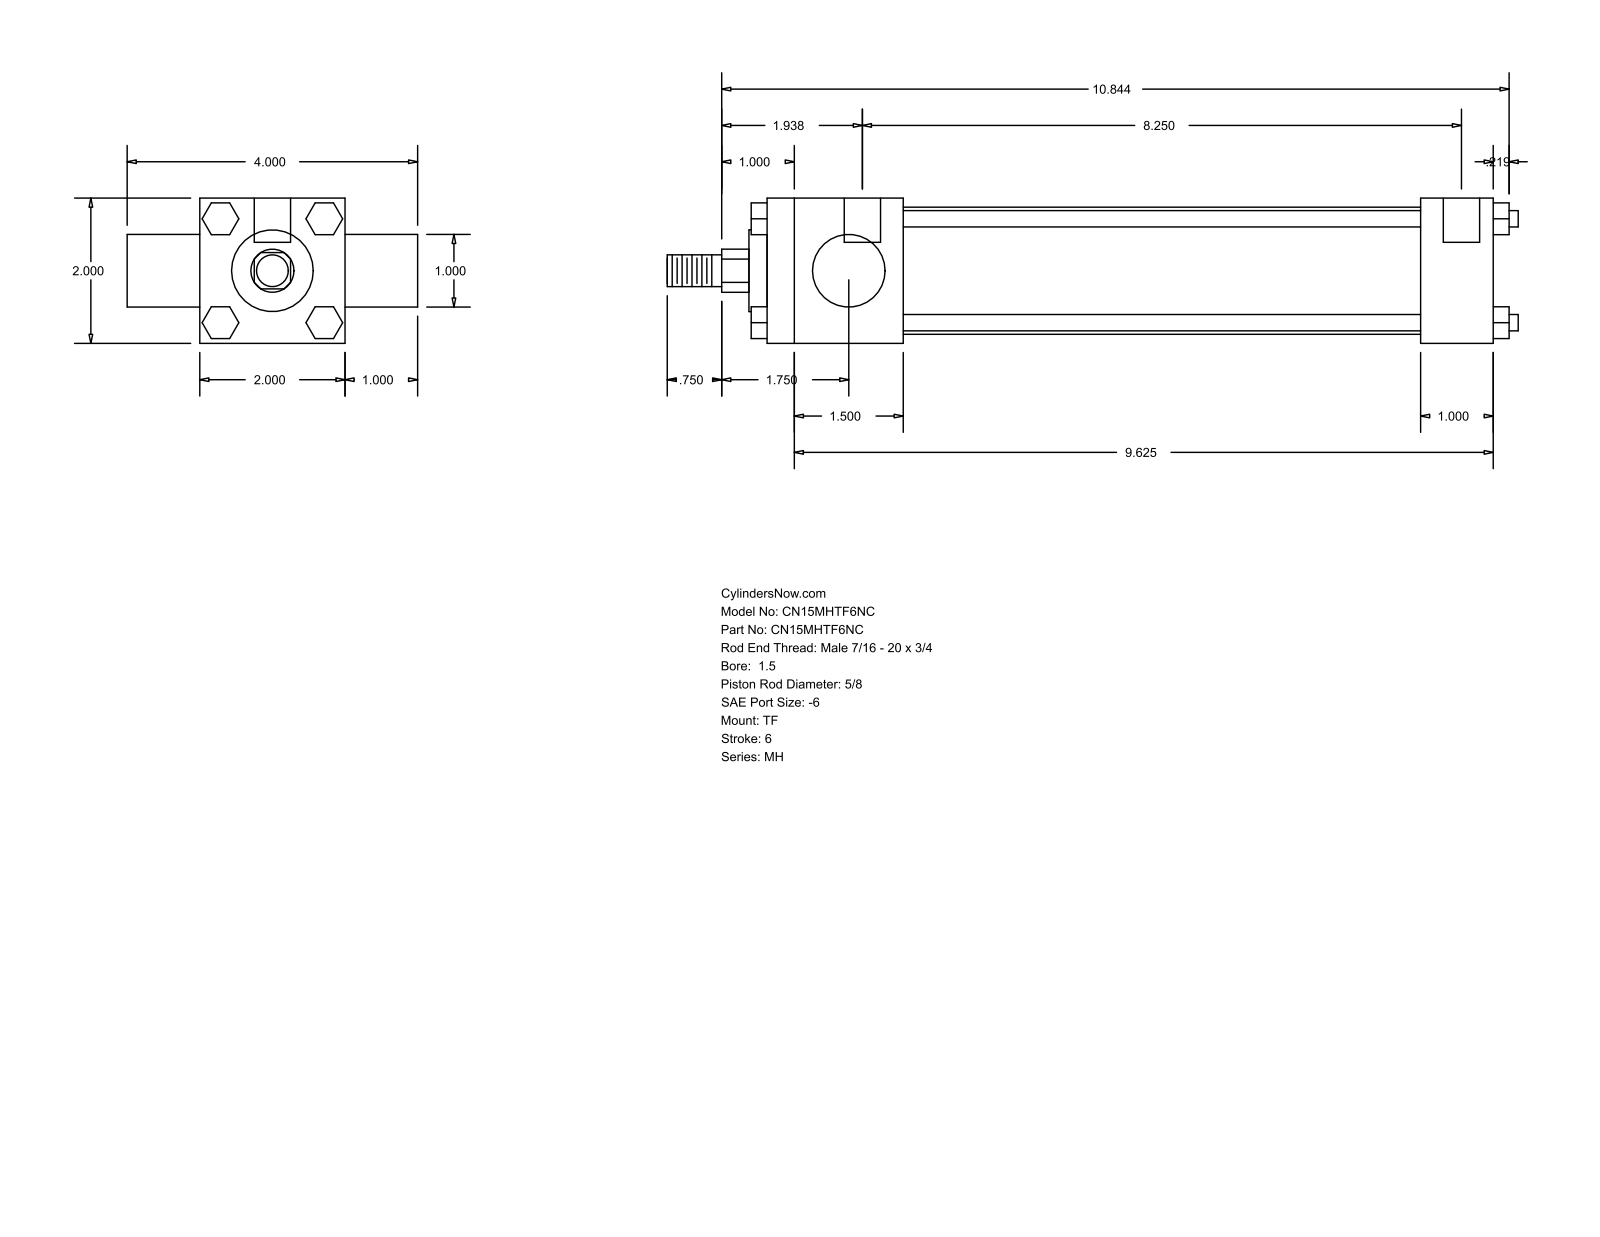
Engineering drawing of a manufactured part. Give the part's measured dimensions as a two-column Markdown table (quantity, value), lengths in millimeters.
| quantity | value |
| --- | --- |
| part name | MH_TF__0150_0.625 |
| STEP written by | GSSL Pune (CONFIG_CONTROL_DESIGN) |
| units | millimeters |
| bodies | 0 solids, 120 faces (92 planar, 28 cylindrical, 0 other) |
| overall size | 297.66 × 101.6 × 50.8 |
| round holes (diameter × count) | 5.56 × 3, 12.7 × 2 |
| round bosses / shafts (diameter × count) | 5.71 × 4, 44.45 × 1, 28.57 × 1, 25.4 × 1, 15.88 × 1, 11.11 × 1 |
| partial cylindrical surfaces (radius × count) | 7.54 × 1 |
| main face-to-face distances | 50.8, 254, 25.4, 76.2, 47.62, 206.38, 228.59, 180.97, 25.41, 11.11 |
| hole center spacings | 3.17, 209.55, 212.72 |
